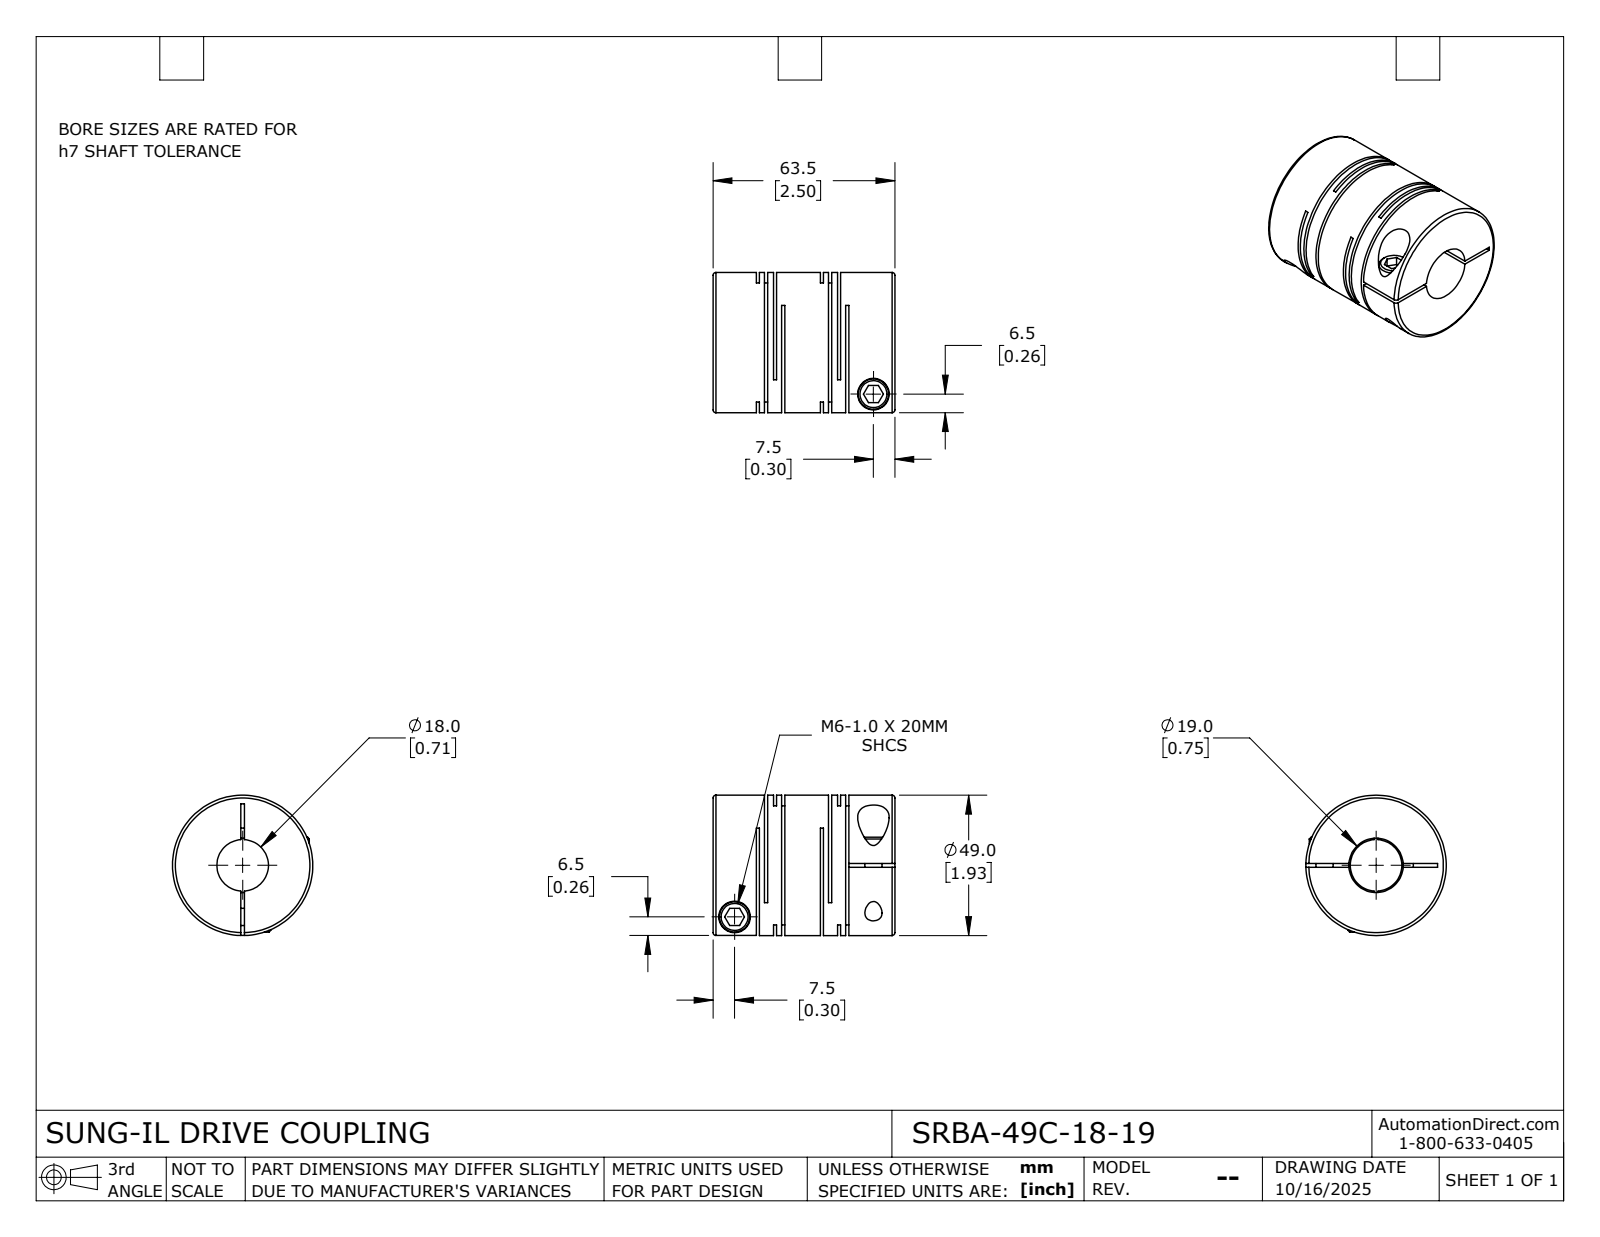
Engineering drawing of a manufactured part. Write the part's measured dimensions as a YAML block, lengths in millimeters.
part_name: "SRBA-49C-18-19"
step_written_by: "SolidWorks 2024 (CONFIG_CONTROL_DESIGN)"
units: millimeters
bodies: {solids: 1, faces: 115, planar: 60, cylindrical: 42, other: 13}
overall_size: [63.5, 49, 49]
volume: 88263
surface_area: 38450
round_holes:
  - {diameter: 6, count: 2}
  - {diameter: 11, count: 2}
  - {diameter: 18, count: 1}
  - {diameter: 19, count: 1}
round_bosses_or_shafts:
  - {diameter: 10.6, count: 2}
  - {diameter: 49, count: 1}
face_to_face_distances: [6, 1.1, 22.35, 2.85, 21.25, 3.15, 1.75, 4.9, 19.5, 16.35]
